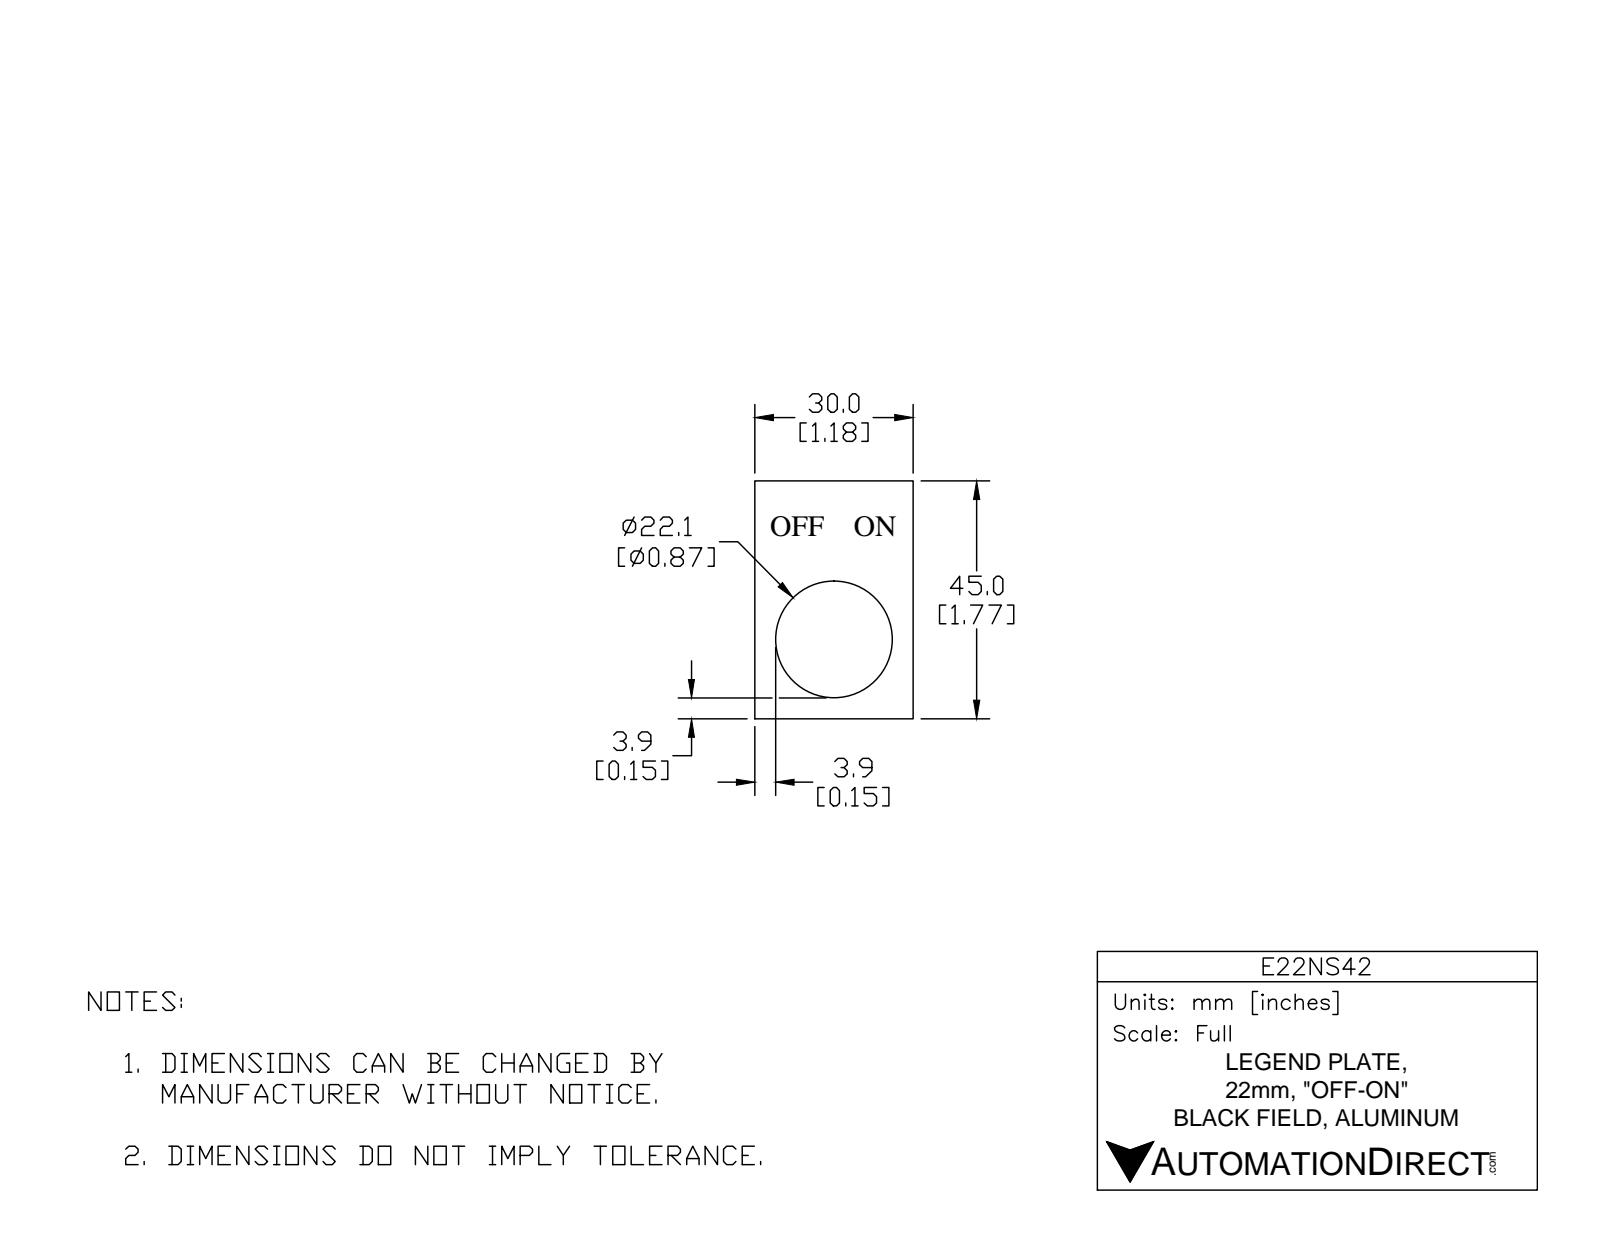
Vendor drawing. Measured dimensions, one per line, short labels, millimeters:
name: E22NS42
written by: SolidWorks 2017 (AUTOMOTIVE_DESIGN)
unit: mm
bodies: 1 solid, 70 faces (51 planar, 3 cylindrical, 16 other)
size: 45 × 30 × 1.3
volume: 1 252 mm³; area: 2 239 mm²
holes: 1× ⌀22.2
face distances: 1.3, 30, 45, 1.05, 4.7, 40.3, 13.4, 16.6, 0.32, 2.12
